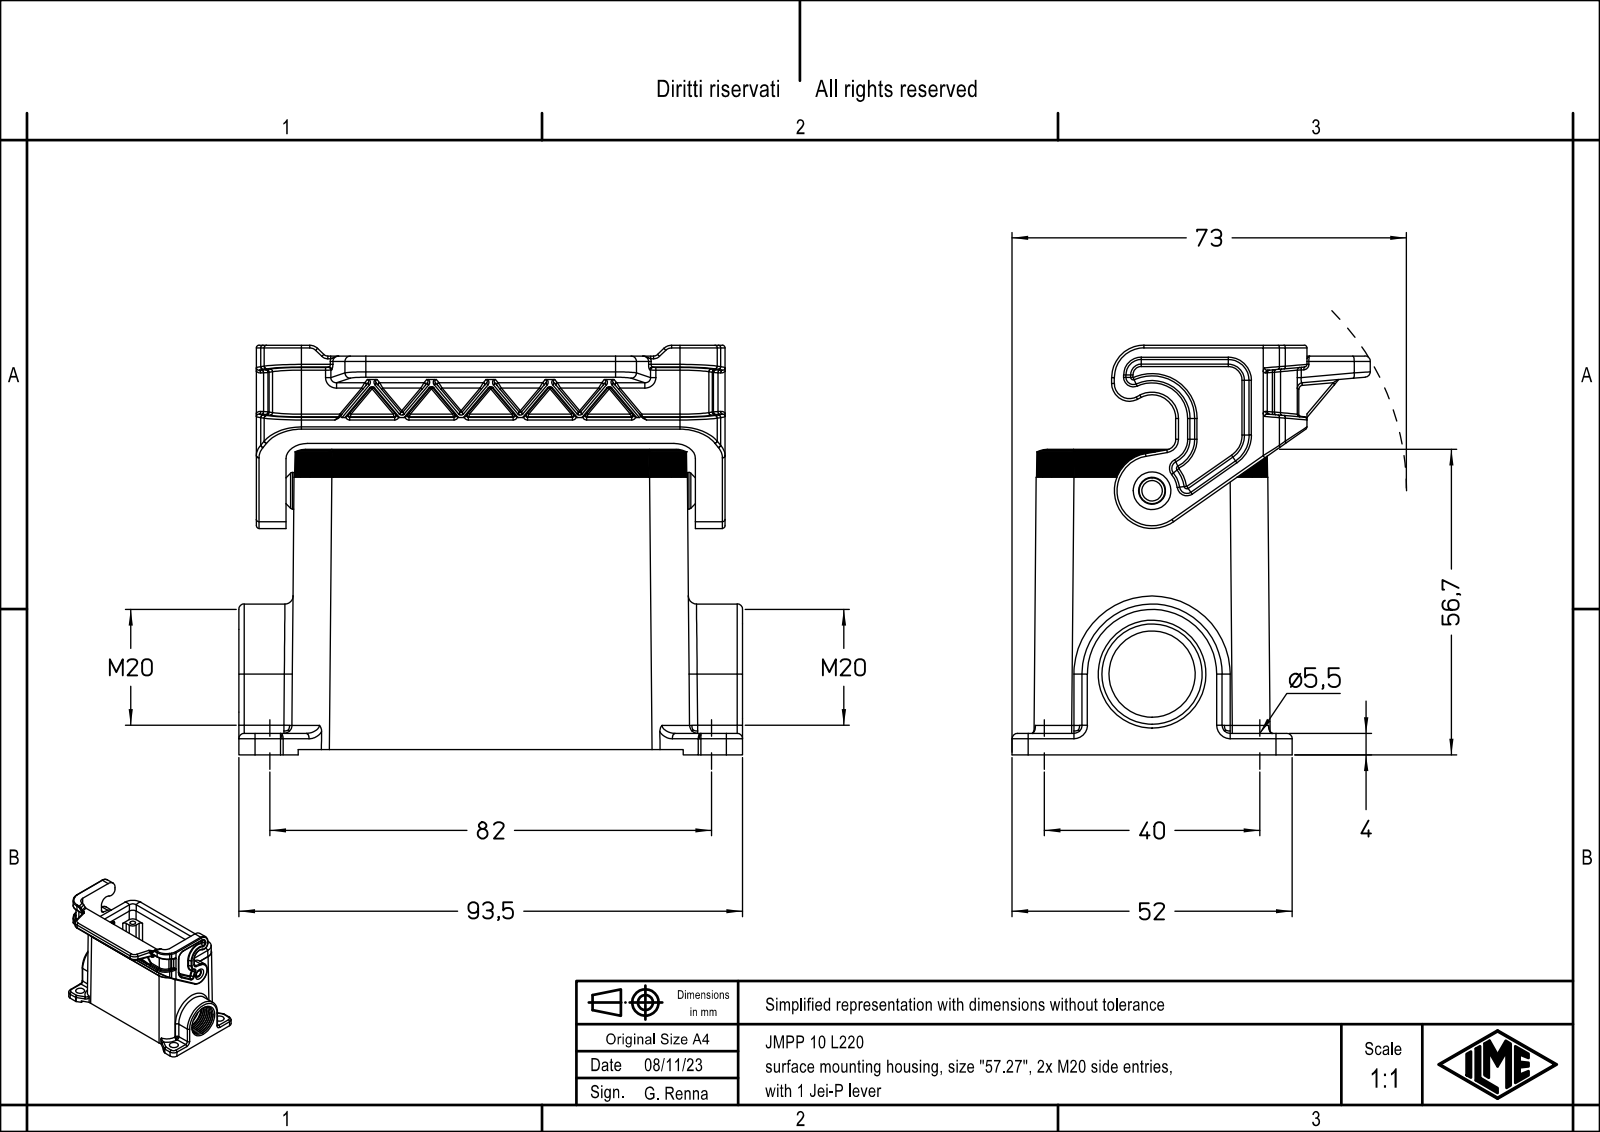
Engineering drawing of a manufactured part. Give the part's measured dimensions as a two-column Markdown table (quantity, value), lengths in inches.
| quantity | value |
| --- | --- |
| part name | JMPP 10 L220 |
| STEP written by | Creo Elements/Direct Modeling 20.1B 02-Apr-2019 (C) Parametric Technology GmbH (AUTOMOTIVE_DESIGN) |
| units | inches |
| bodies | 1 solid, 789 faces (169 planar, 326 cylindrical, 294 other) |
| overall size | 3.681 × 2.992 × 2.618 |
| volume | 5.594 in³ |
| surface area | 65.93 in² |
| round holes (diameter × count) | 0.118 × 4, 0.138 × 4, 0.217 × 4, 0.189 × 1, 0.63 × 1, 0.732 × 1 |
| round bosses / shafts (diameter × count) | 0.268 × 1 |
| partial cylindrical surfaces (radius × count) | 0.02 × 77, 0.012 × 71, 0.039 × 27, 0.059 × 16, 0.118 × 16, 0.079 × 10, 0.276 × 9, 0.157 × 8 |
| main face-to-face distances | 0.118, 0.039, 0.157, 2.992, 2.913, 2.874, 2.756, 0.079, 0.344, 3.337 |
| hole center spacings | 0.555, 1.408, 2.748, 3.037, 1.063, 1.575, 2.244, 2.483 |
